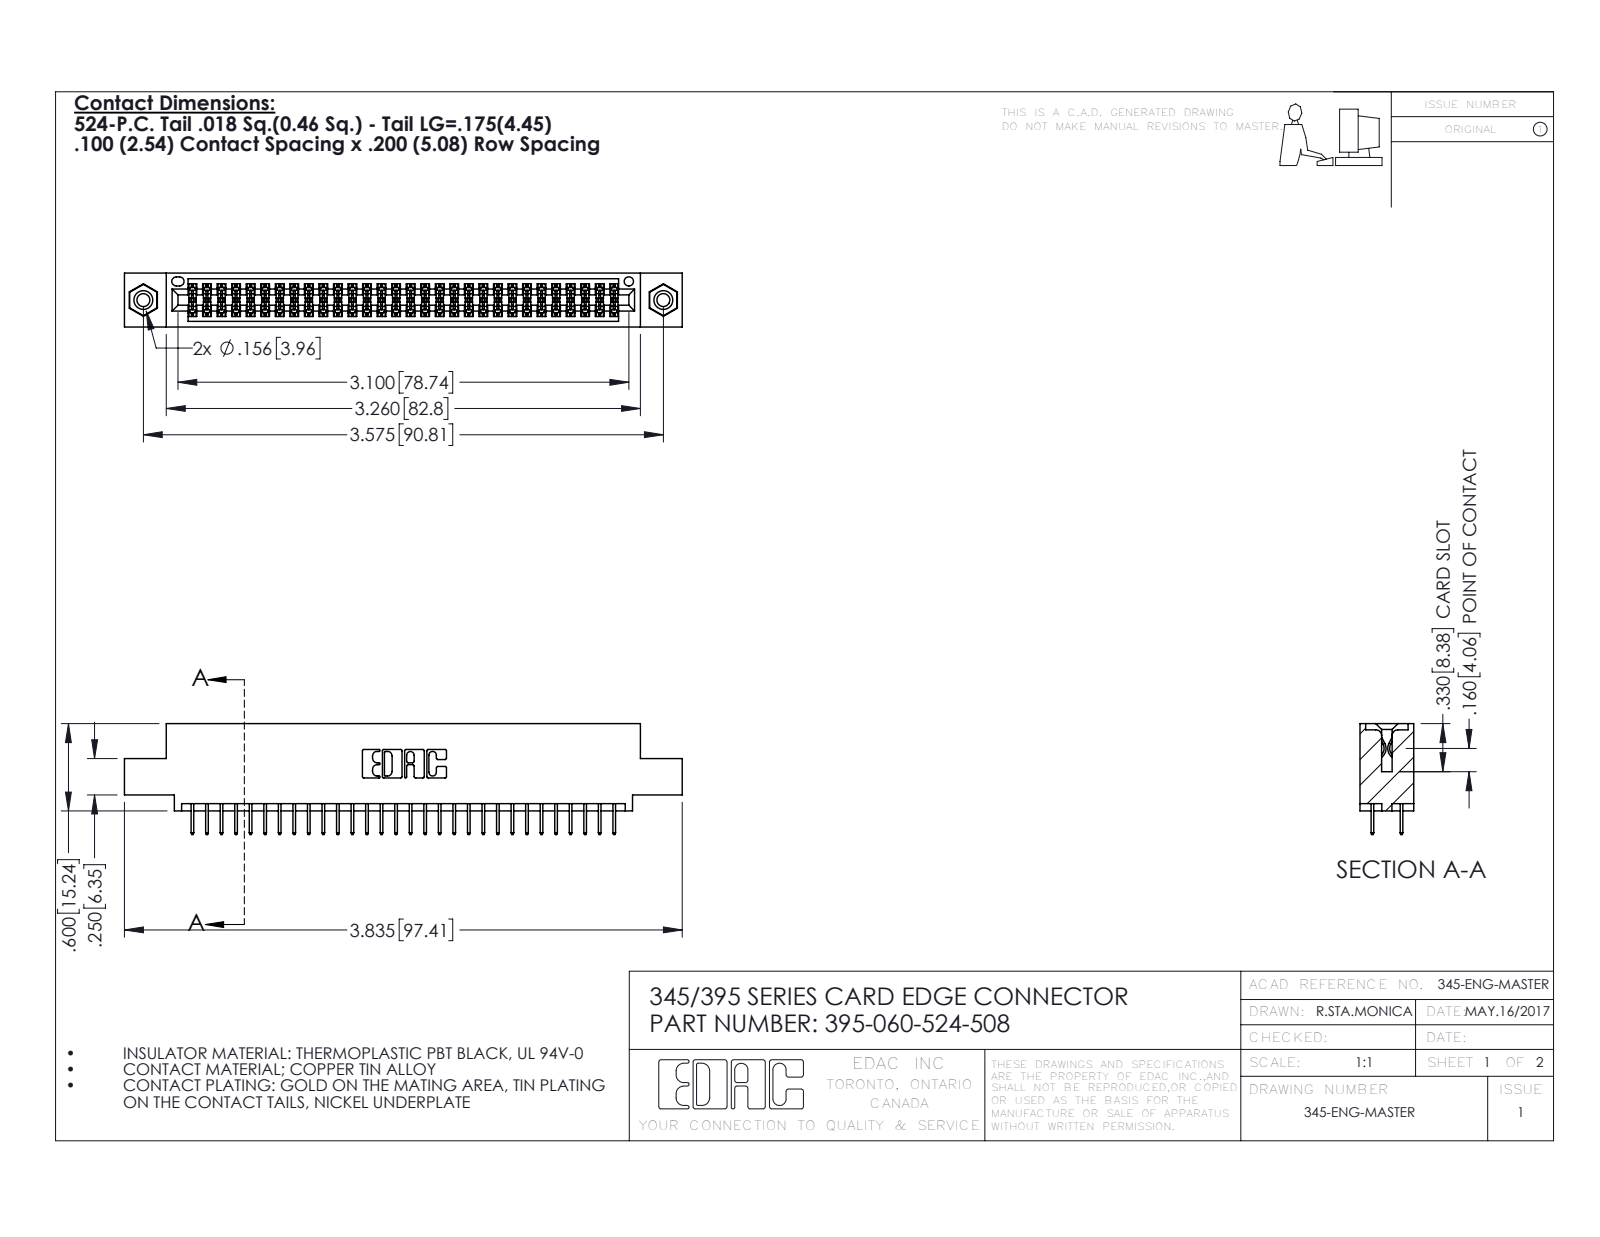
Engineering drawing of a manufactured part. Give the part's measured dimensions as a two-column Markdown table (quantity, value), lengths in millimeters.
| quantity | value |
| --- | --- |
| part name | 345-292-001_345-293-124; 345 Part_0.110 Offset - 0.156 Dia-TI; 345-250-001_345-250-003-102; 395-060-524-508 |
| STEP written by | SolidWorks 2016 (CONFIG_CONTROL_DESIGN) |
| units | millimeters |
| bodies | 63 solids, 3430 faces (2456 planar, 958 cylindrical, 16 other) |
| overall size | 97.4 × 19.4 × 9.4 |
| volume | 9 180 mm³ |
| surface area | 13 210 mm² |
| round holes (diameter × count) | 2.3 × 2, 3.2 × 2, 4 × 2, 1.6 × 1 |
| round bosses / shafts (diameter × count) | 3.9 × 2 |
| partial cylindrical surfaces (radius × count) | 0.2 × 90, 0.3 × 22, 0.2 × 6, 0.8 × 6, 0.7 × 3, 0.4 × 2, 0.5 × 2, 0.6 × 2 |
| main face-to-face distances | 1.8, 7.6, 5.1, 9.4, 2.5, 6.9, 0.6, 5.7, 1.8, 4.4 |
| hole center spacings | 6.9, 84.8, 90.8 |
